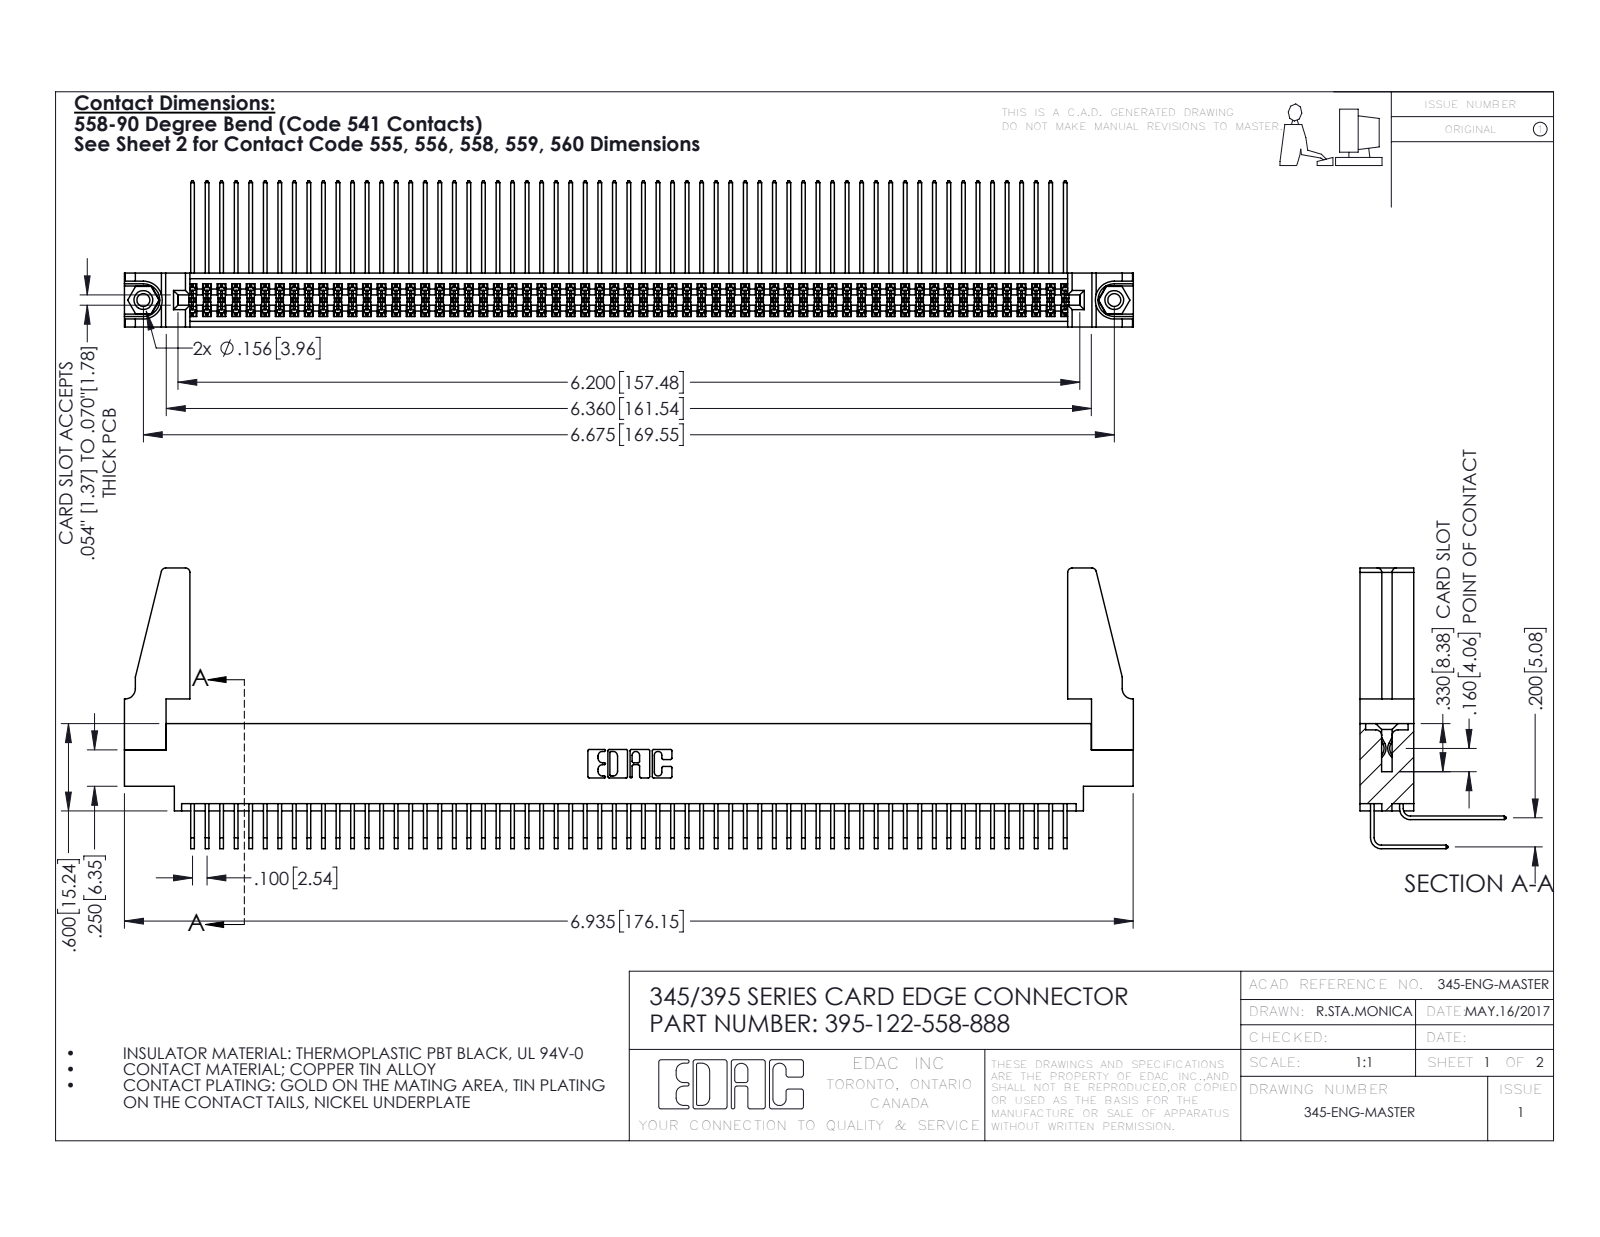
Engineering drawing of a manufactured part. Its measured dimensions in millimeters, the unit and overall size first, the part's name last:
Units: millimetres
Overall size (bounding box): 176.2 × 49 × 25.5
Round holes (diameter × count): ⌀2.3 ×2, ⌀3.2 ×2, ⌀4 ×2, ⌀1.6 ×1
Round bosses / shafts (diameter × count): ⌀3.9 ×2
Partial cylindrical surfaces — rounded edges, fillets, slot ends (radius × count): R0.2 ×183, R0.3 ×22, R0.8 ×8, R0.2 ×6, R0.8 ×6, R0.7 ×3, R0.4 ×2, R0.5 ×2
Main face-to-face distances: 1.8, 7.6, 5.1, 9.4, 2.5, 6.9, 0.6, 5.7, 4.4, 0.6
Hole centre spacings: 6.9, 163.6, 169.5
Volume: 21 140 mm³ · Surface area: 33 370 mm²
Bodies: 127 solids, 6598 faces (4426 planar, 2156 cylindrical, 16 other)
Part name (STEP PRODUCT): 345-250-001_345-250-001-102; 345-292-001_558 559 Tail - 1; 345 Part_0.170 Offset - 0.156 Dia-TH; 345-220-078_345-220-088 (+2 more)
STEP written by: SolidWorks 2016 (CONFIG_CONTROL_DESIGN)
